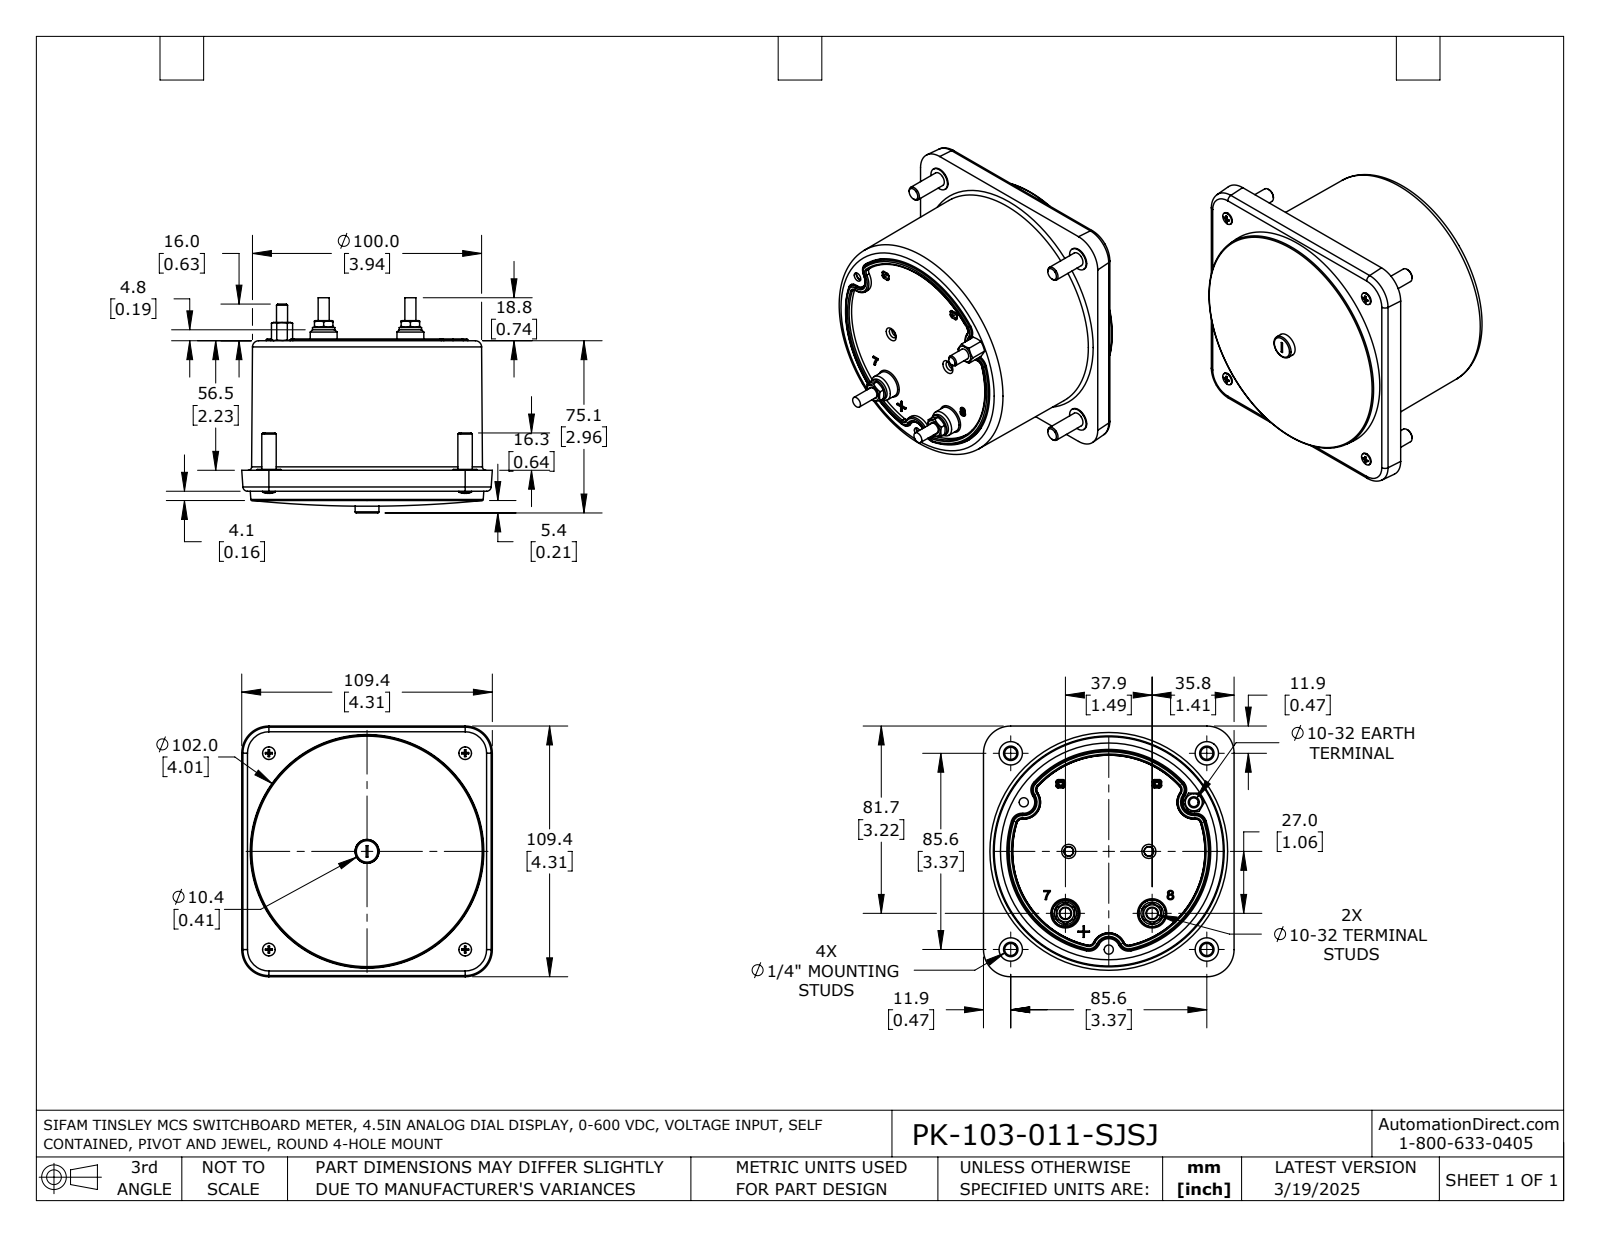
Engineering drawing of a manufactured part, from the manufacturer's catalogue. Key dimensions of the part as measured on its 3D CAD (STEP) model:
Part name (STEP PRODUCT): PK-103-011-SJSJ
STEP written by: SolidWorks 2021 (AUTOMOTIVE_DESIGN)
Units: inches
Bodies: 1 solid, 609 faces (167 planar, 141 cylindrical, 301 other)
Overall size (bounding box): 4.307 × 4.307 × 3.697
Volume: 36.28 in³ · Surface area: 82.21 in²
Round holes (diameter × count): ⌀0.094 ×4, ⌀0.138 ×4, ⌀0.315 ×4, ⌀0.157 ×3, ⌀0.209 ×2
Round bosses / shafts (diameter × count): ⌀0.402 ×4, ⌀0.248 ×4, ⌀0.217 ×4, ⌀0.114 ×4, ⌀0.19 ×3, ⌀0.384 ×2, ⌀0.146 ×1
Partial cylindrical surfaces — rounded edges, fillets, slot ends (radius × count): R0.02 ×24, R0.189 ×9, R0.079 ×4, R1.752 ×1
Main face-to-face distances: 2.177, 2.537, 0.36, 0.048, 2.225, 2.585, 0.489, 2.715, 2.667, 0.129
Hole centre spacings: 3.372, 3.37, 3.374, 3.378, 3.38, 4.769, 0.971, 1.126
